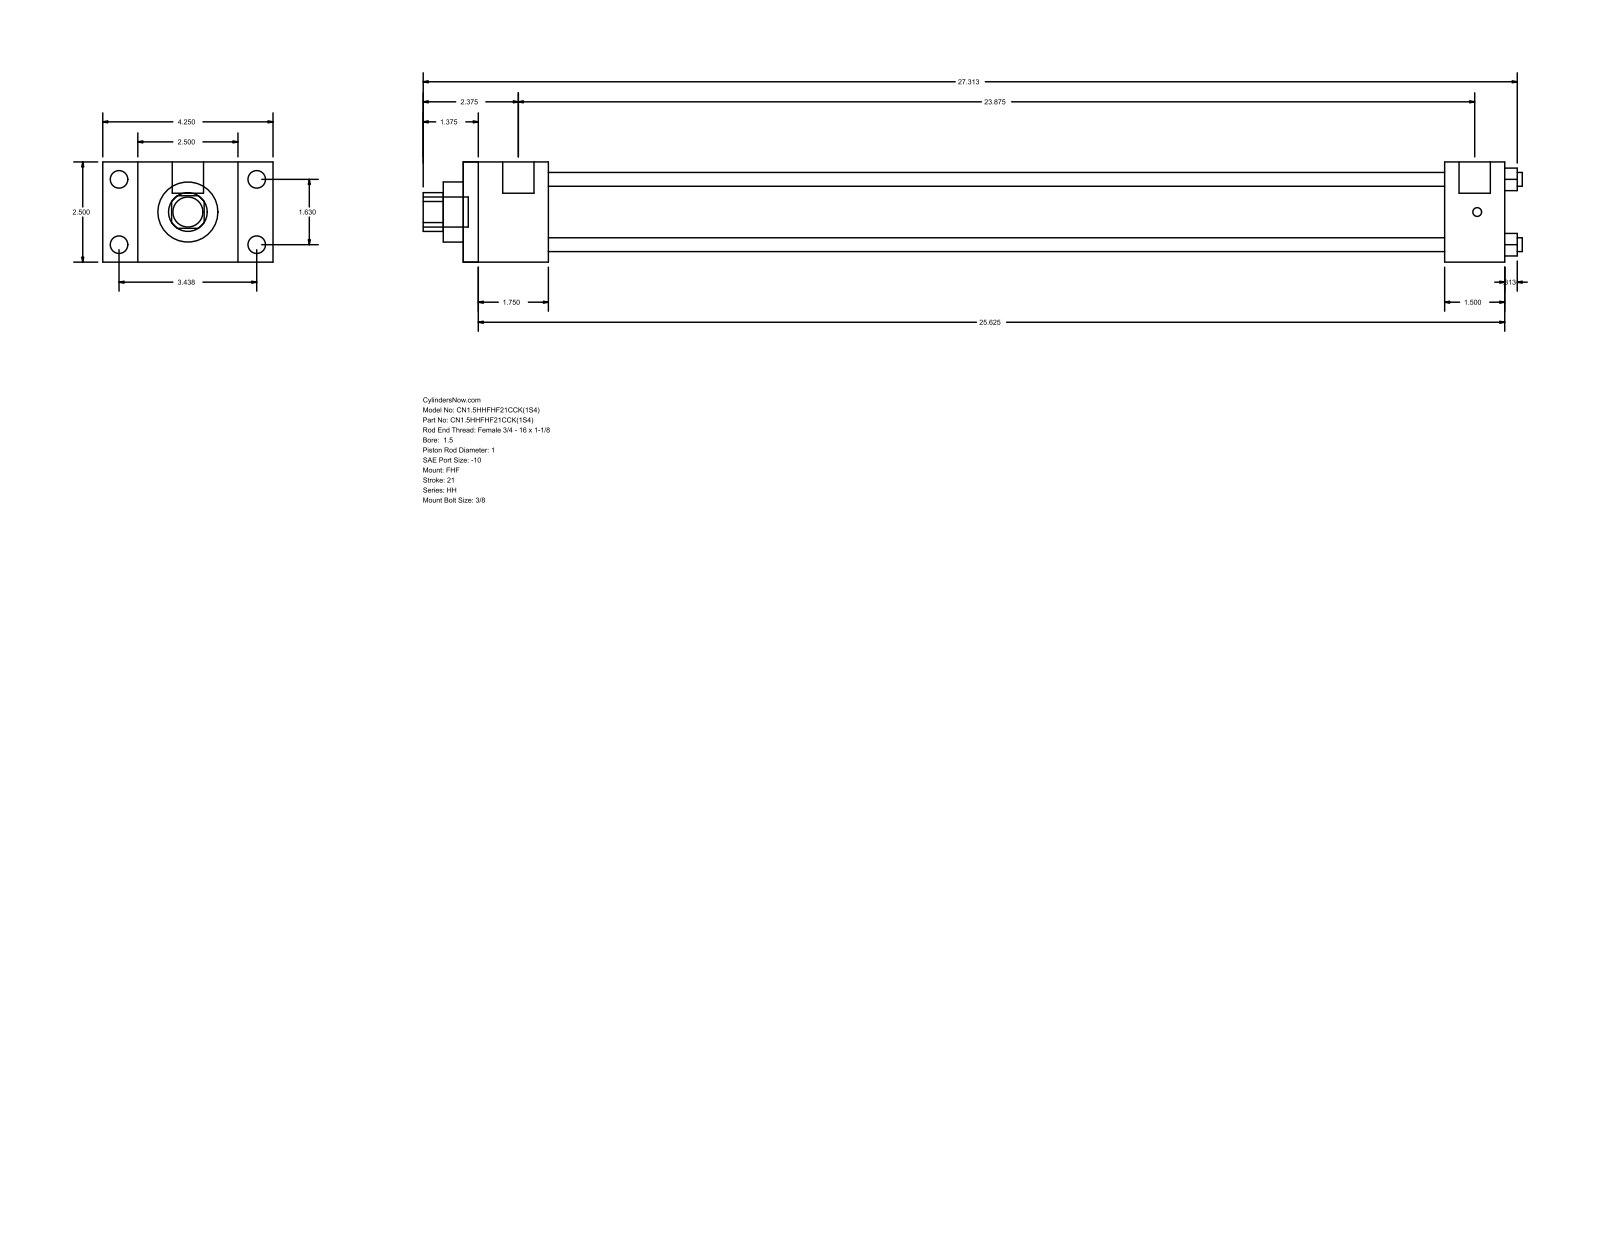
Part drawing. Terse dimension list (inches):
name: HH_FHF__0150_1
written by: GSSL Pune (CONFIG_CONTROL_DESIGN)
unit: in
bodies: 0 solids, 88 faces (60 planar, 28 cylindrical, 0 other)
size: 27.437 × 4.25 × 2.5
holes: 4× ⌀0.345, 1× ⌀1, 1× ⌀1.5, 1× ⌀1.75
bosses: 4× ⌀0.438, 4× ⌀0.219, 2× ⌀0.781, 1× ⌀0.75
rounds: 1× R0.484
face distances: 2.5, 0.875, 3.375, 2.125, 4.25, 26, 23.875, 24.5, 22.375, 1.5
hole spacings: 1.152, 1.63, 2.305
